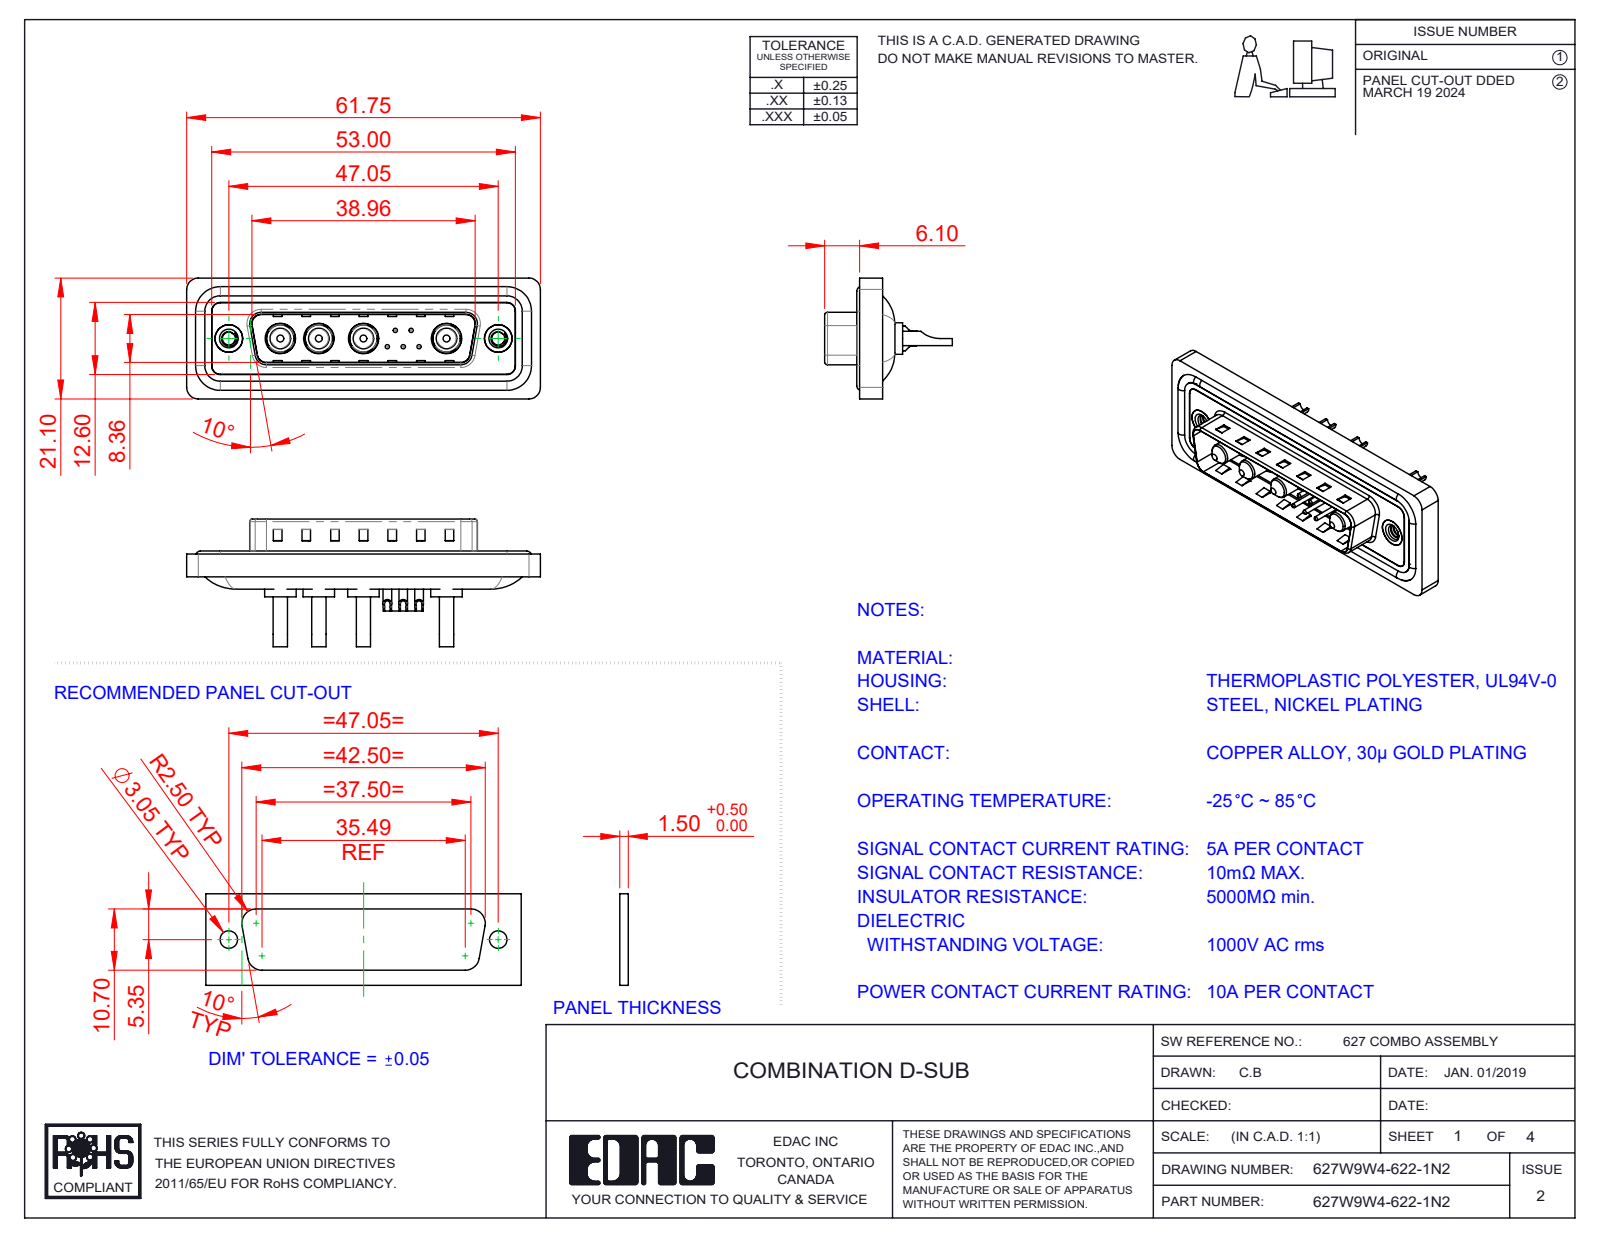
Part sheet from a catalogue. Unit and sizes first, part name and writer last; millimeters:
Units: millimetres
Overall size (bounding box): 61.75 × 22.3 × 21.1
Round holes (diameter × count): ⌀0.75 ×5, ⌀1 ×5, ⌀1.6 ×5, ⌀2 ×5, ⌀1.7 ×4, ⌀4.85 ×4, ⌀5.3 ×4, ⌀2.26 ×2, ⌀4 ×2, ⌀4.8 ×2, ⌀5 ×2
Round bosses / shafts (diameter × count): ⌀1.5 ×5, ⌀5.5 ×4, ⌀5.2 ×4, ⌀4.75 ×4, ⌀3.75 ×4, ⌀3.6 ×4, ⌀2.5 ×4, ⌀1.6 ×4
Partial cylindrical surfaces — rounded edges, fillets, slot ends (radius × count): R1.5 ×22, R2 ×18, R0.5 ×8, R1.6 ×8, R1 ×6, R0.25 ×4, R0.6 ×4, R0.65 ×4
Main face-to-face distances: 0.4, 1.5, 1.1, 0.5, 1.6, 3.1, 2.9, 0.82, 9.58, 5.65
Hole centre spacings: 3.16, 2.77, 5.04, 14.51, 2.78, 4.4, 4.41, 5
Volume: 7 401 mm³ · Surface area: 12 066 mm²
Bodies: 20 solids, 848 faces (302 planar, 356 cylindrical, 190 other)
Part name (STEP PRODUCT): 627Combo Threaded Rivet_2; 627Combo Housing_9W4; 627Combo Shell Front_25 Contacts; 627Combo Shell Rear_25 Contacts (+5 more)
STEP written by: SolidWorks 2023 (CONFIG_CONTROL_DESIGN)
